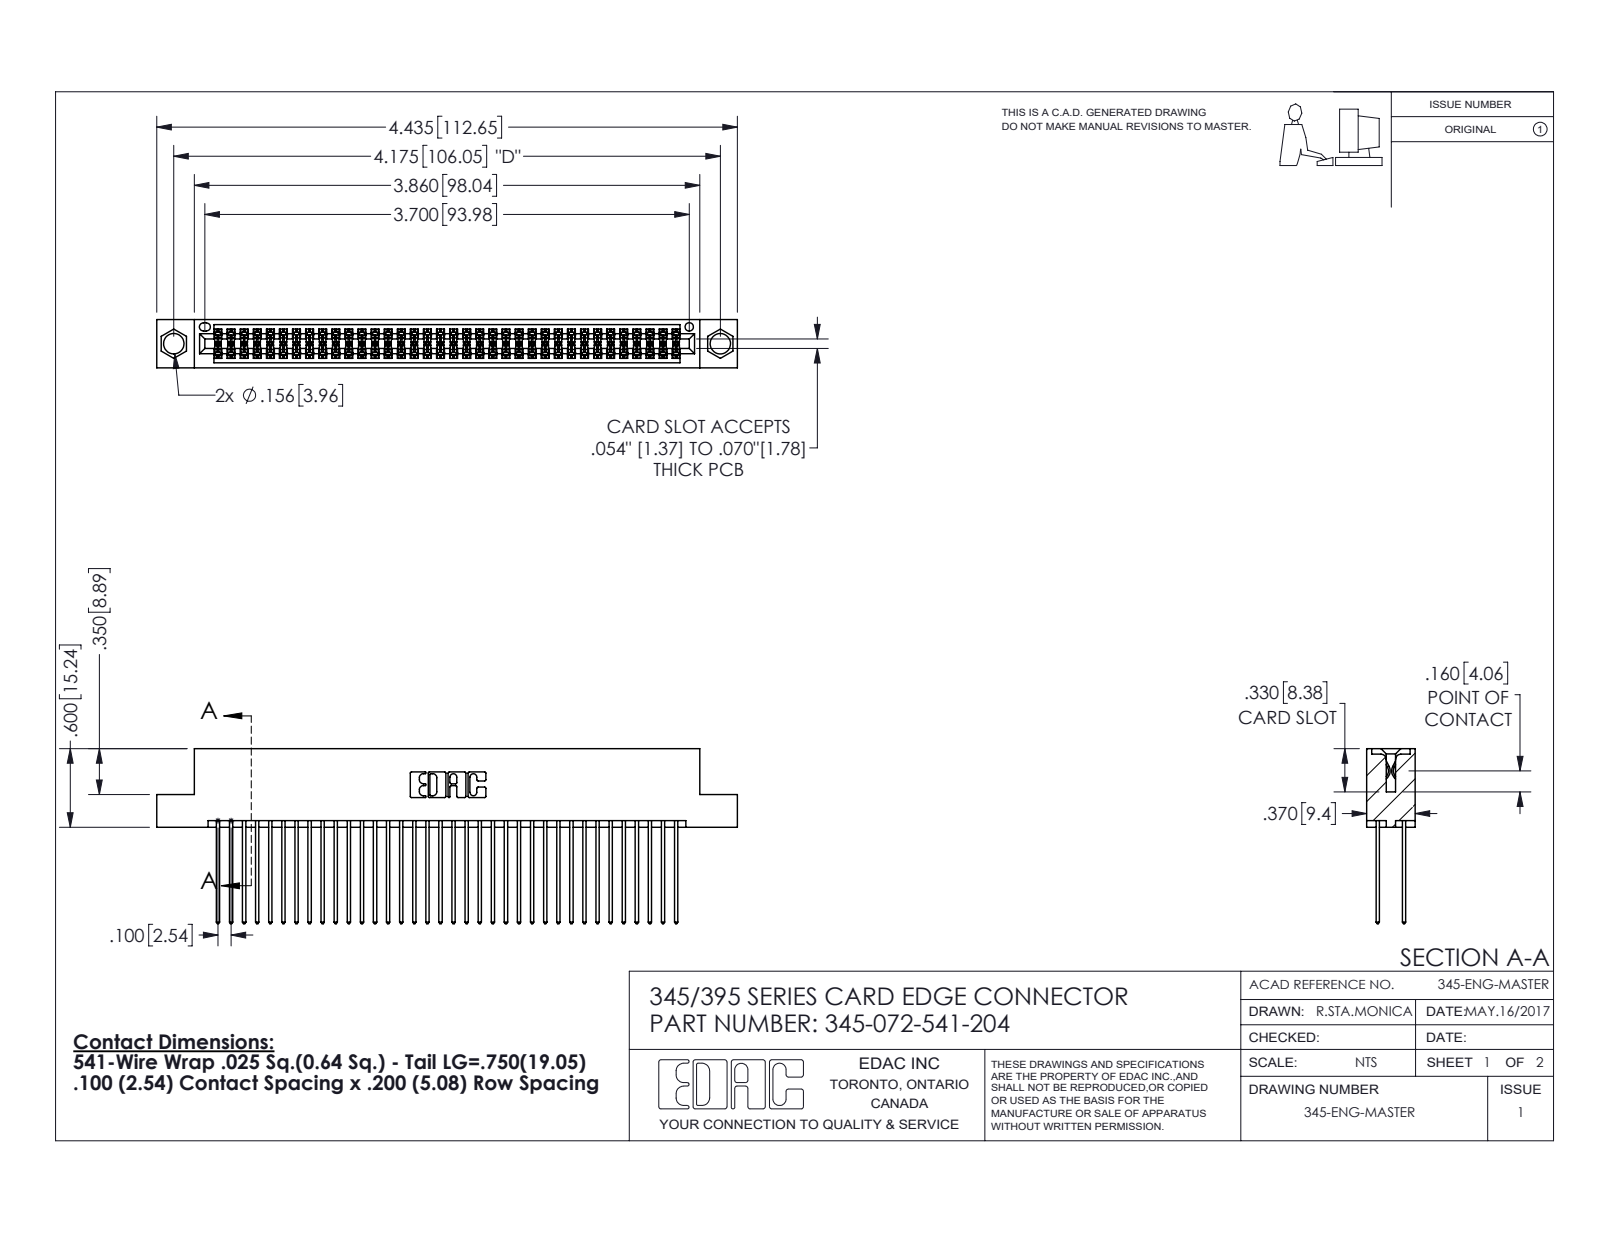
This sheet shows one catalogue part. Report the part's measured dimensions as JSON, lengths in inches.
{"part_name": "345-292-001_345-293-141; 345 Part_Flush Mounting Lugs - 0.156 Dia-TI; 345-072-541-204", "step_written_by": "SolidWorks 2020 (CONFIG_CONTROL_DESIGN)", "units": "inches", "bodies": {"solids": 73, "faces": 3740, "planar": 2470, "cylindrical": 1270, "other": 0}, "overall_size": [4.435, 1.337, 0.37], "volume_in3": 0.683, "surface_area_in2": 28.25, "round_holes": [[0.156, 2], [0.064, 1]], "partial_cylinders_radius": [[0.006, 108], [0.01, 72], [0.01, 22], [0.007, 6], [0.031, 6], [0.026, 3], [0.014, 2], [0.019, 2]], "face_to_face_distances": [0.298, 0.072, 0.2, 0.098, 0.272, 0.025, 0.225, 0.37, 0.175, 0.149], "hole_center_spacings": [0.27, 3.939, 4.175]}
